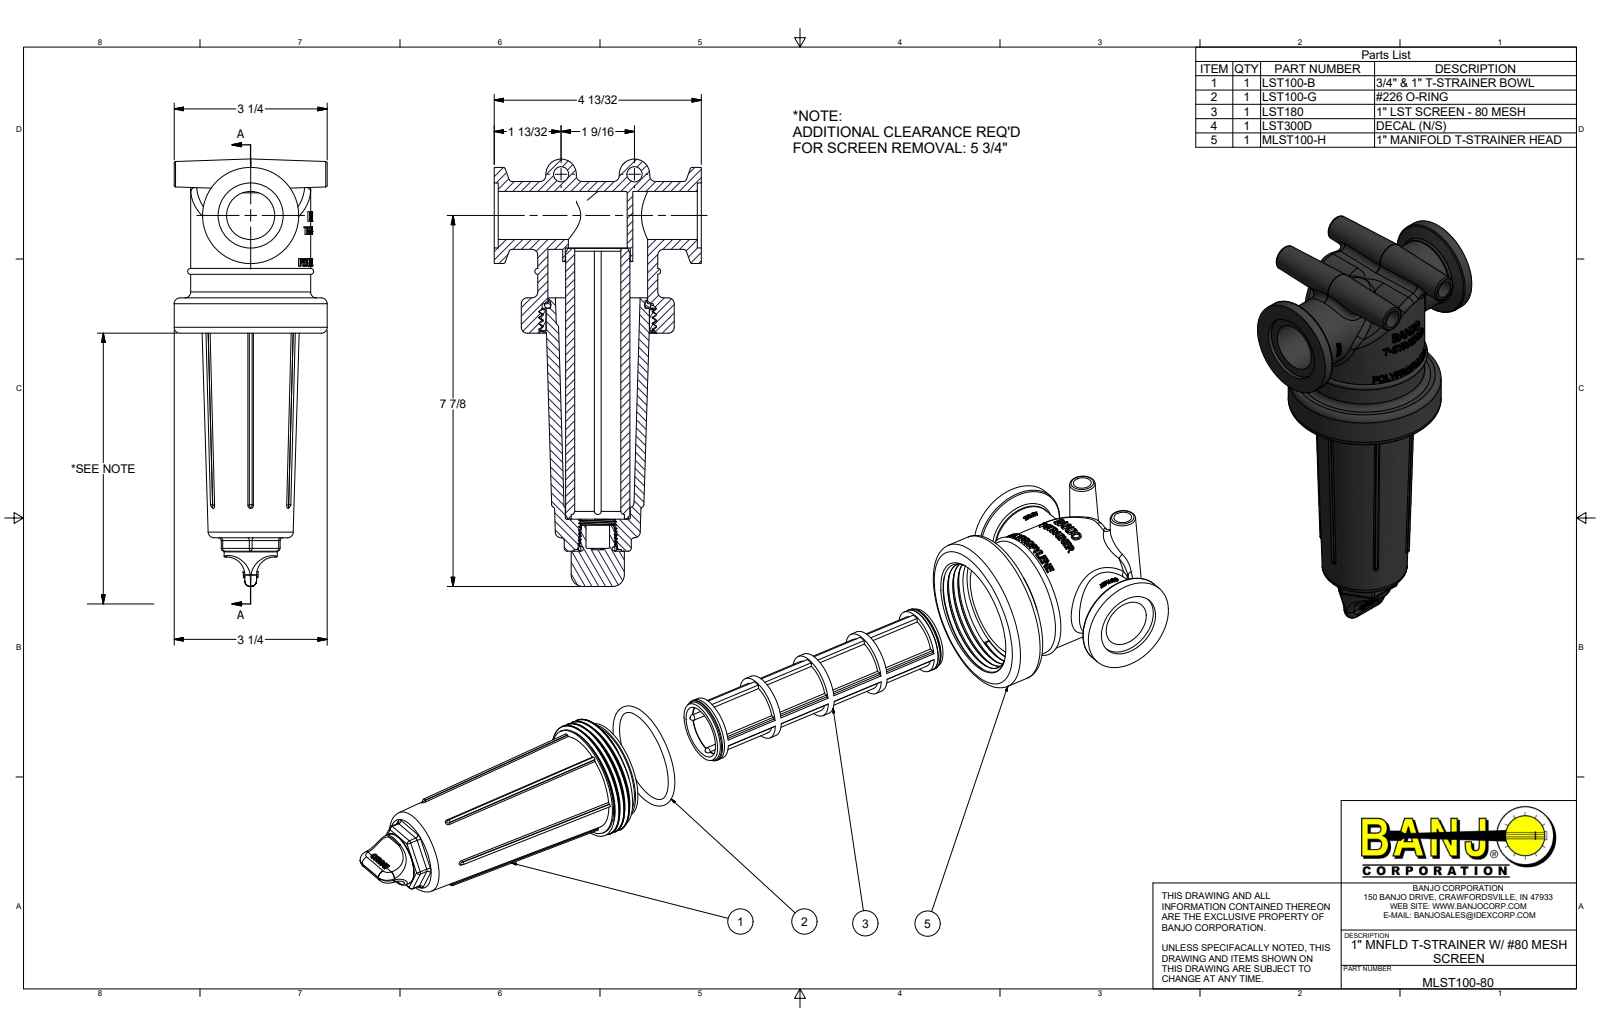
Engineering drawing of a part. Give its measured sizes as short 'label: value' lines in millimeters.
name: MLST100-80; MLST100-H; LST100-B; LST100-XB (+4 more)
written by: Autodesk Inventor 2013 (AUTOMOTIVE_DESIGN)
unit: mm
bodies: 7 solids, 1343 faces (689 planar, 160 cylindrical, 494 other)
size: 230.6 × 111.8 × 82.6
volume: 310 400 mm³; area: 163 000 mm²
holes: 2× ⌀35.1, 1× ⌀12.7, 1× ⌀24.9, 1× ⌀25.5, 1× ⌀25.9, 1× ⌀27.9, 1× ⌀31.8, 1× ⌀53.8, 1× ⌀55.8, 1× ⌀60.1
bosses: 1× ⌀82.6, 1× ⌀64.8, 1× ⌀63.5, 1× ⌀59.4, 1× ⌀53.3, 1× ⌀51.8, 1× ⌀51.1, 1× ⌀37.8
rounds: 19× R1.5, 9× R0.8, 4× R1.9, 2× R9.7, 1× R12.7, 1× R19.1, 1× R33.4
face distances: 1.3, 34.3, 6.4, 0.8, 12.2, 19.1, 30.5, 3.8, 38.1, 54
